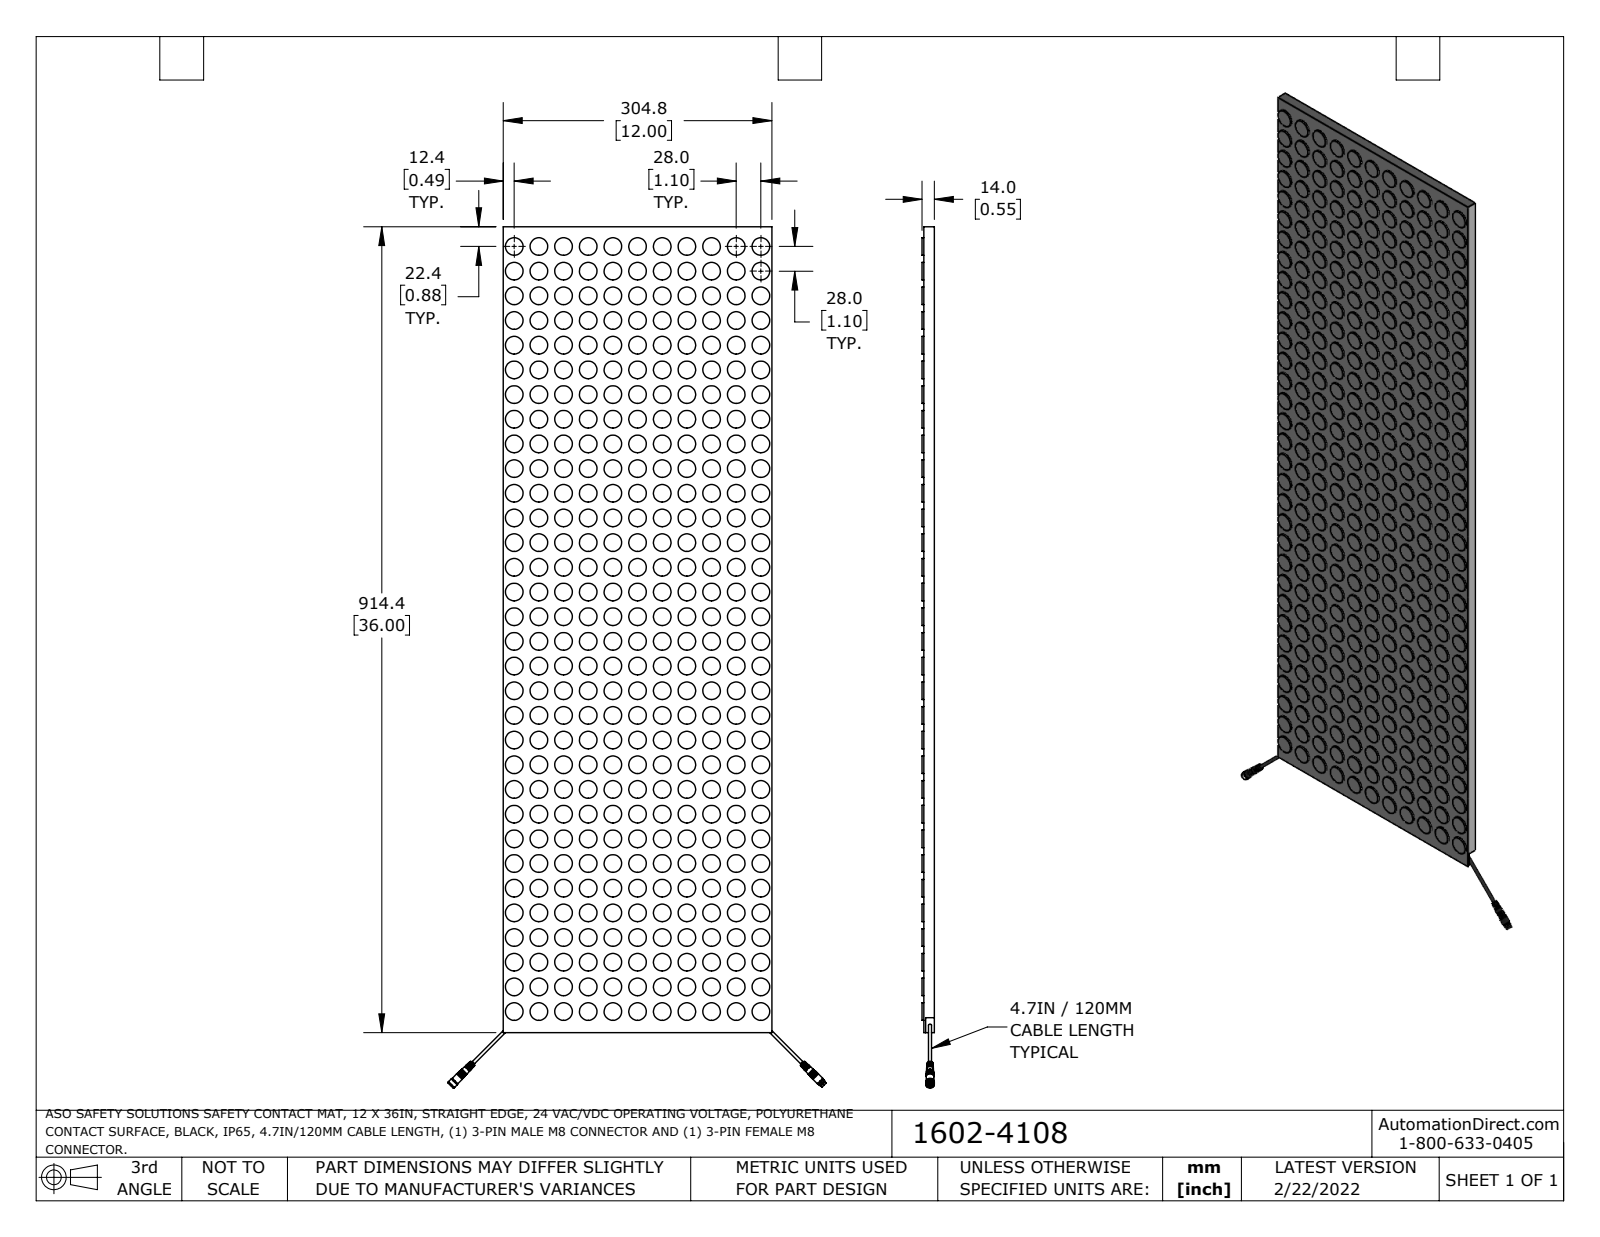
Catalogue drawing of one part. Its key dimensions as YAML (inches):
part_name: "1602-4108_Default"
step_written_by: "SolidWorks 2021 (CONFIG_CONTROL_DESIGN)"
units: inches
bodies: {solids: 20, faces: 1440, planar: 480, cylindrical: 822, other: 138}
overall_size: [38.474, 16.904, 0.551]
volume: 217.7
surface_area: 986.1
round_holes:
  - {diameter: 0.063, count: 3}
  - {diameter: 0.134, count: 2}
  - {diameter: 0.228, count: 1}
  - {diameter: 0.232, count: 1}
  - {diameter: 0.272, count: 1}
  - {diameter: 0.283, count: 1}
round_bosses_or_shafts:
  - {diameter: 0.787, count: 352}
  - {diameter: 0.047, count: 24}
  - {diameter: 0.031, count: 8}
  - {diameter: 0.039, count: 3}
  - {diameter: 0.346, count: 2}
  - {diameter: 0.138, count: 2}
  - {diameter: 0.378, count: 1}
  - {diameter: 0.354, count: 1}
face_to_face_distances: [0.472, 0.079, 0.551, 12, 36, 0.087, 0.394, 0.157, 0.173, 0.039]
hole_center_spacings: [0.069, 0.098, 0.138]
